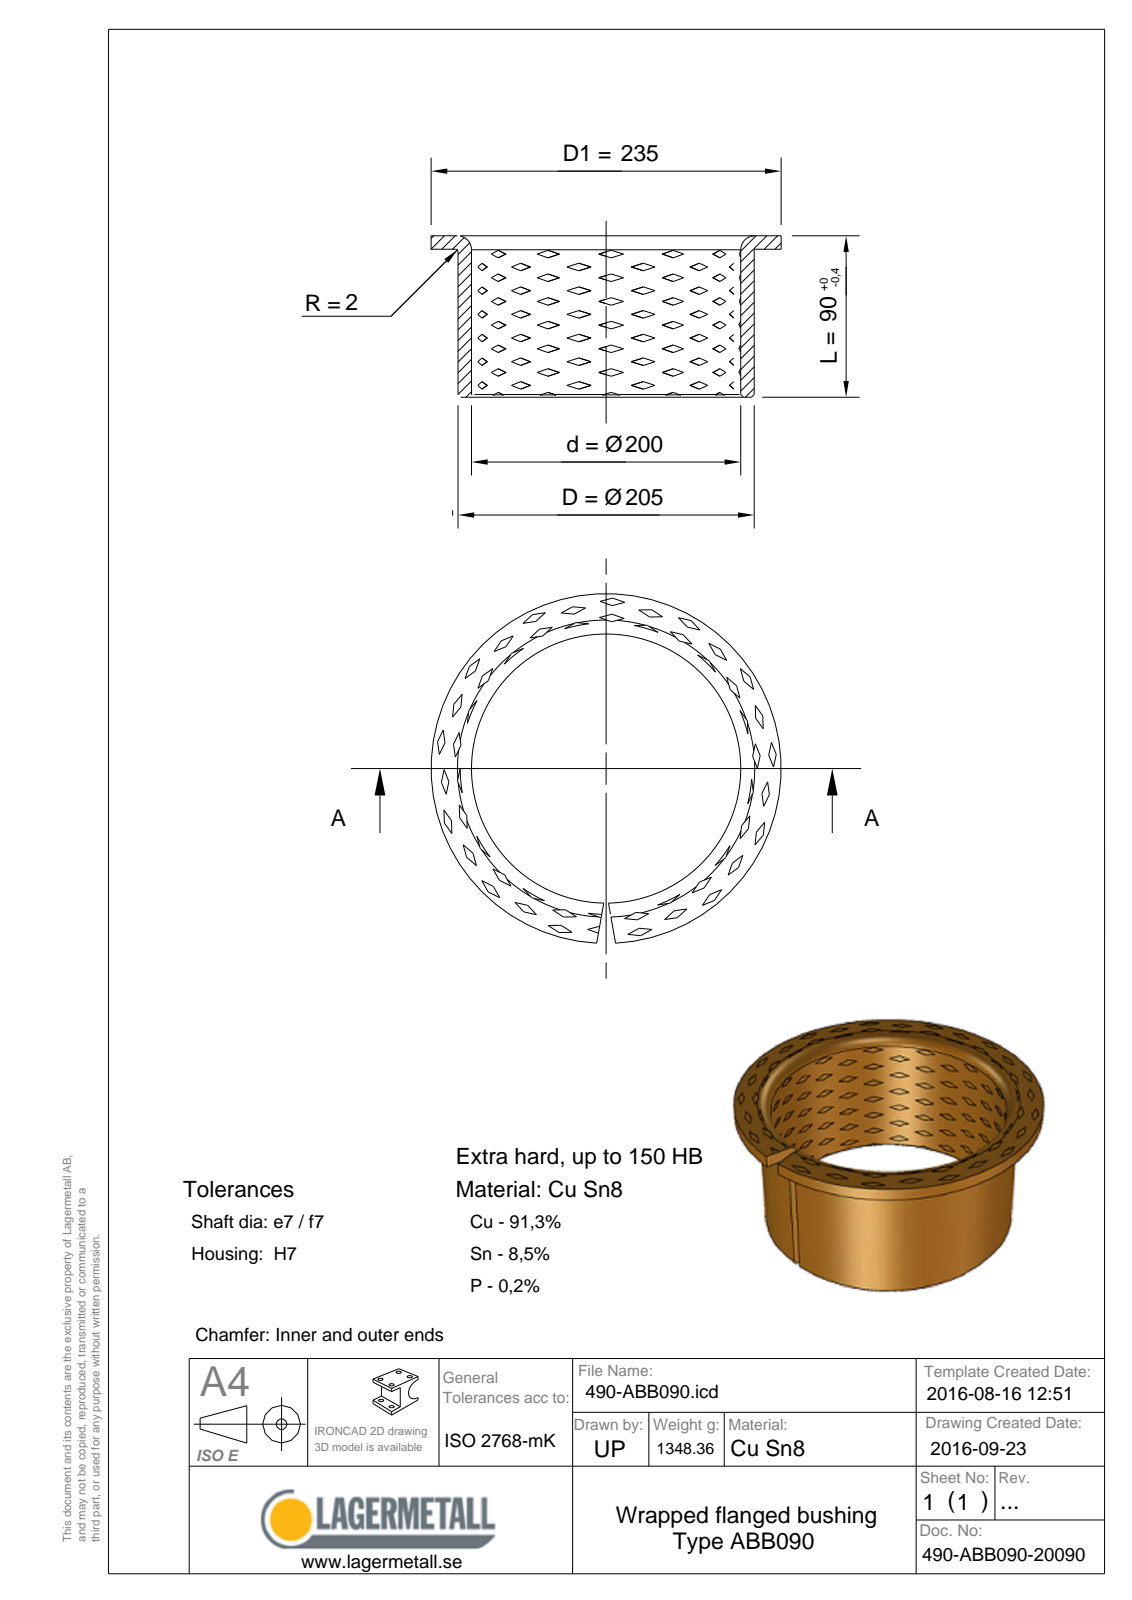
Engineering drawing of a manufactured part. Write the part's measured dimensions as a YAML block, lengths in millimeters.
step_written_by: "Spatial InterOp 3D (CONFIG_CONTROL_DESIGN)"
units: millimeters
bodies: {solids: 1, faces: 26, planar: 5, cylindrical: 9, other: 12}
overall_size: [235, 235, 90]
volume: 166464
surface_area: 136859
round_holes:
  - {diameter: 200, count: 1}
round_bosses_or_shafts:
  - {diameter: 235, count: 1}
  - {diameter: 205, count: 1}
face_to_face_distances: [2.5, 87.5, 90]
